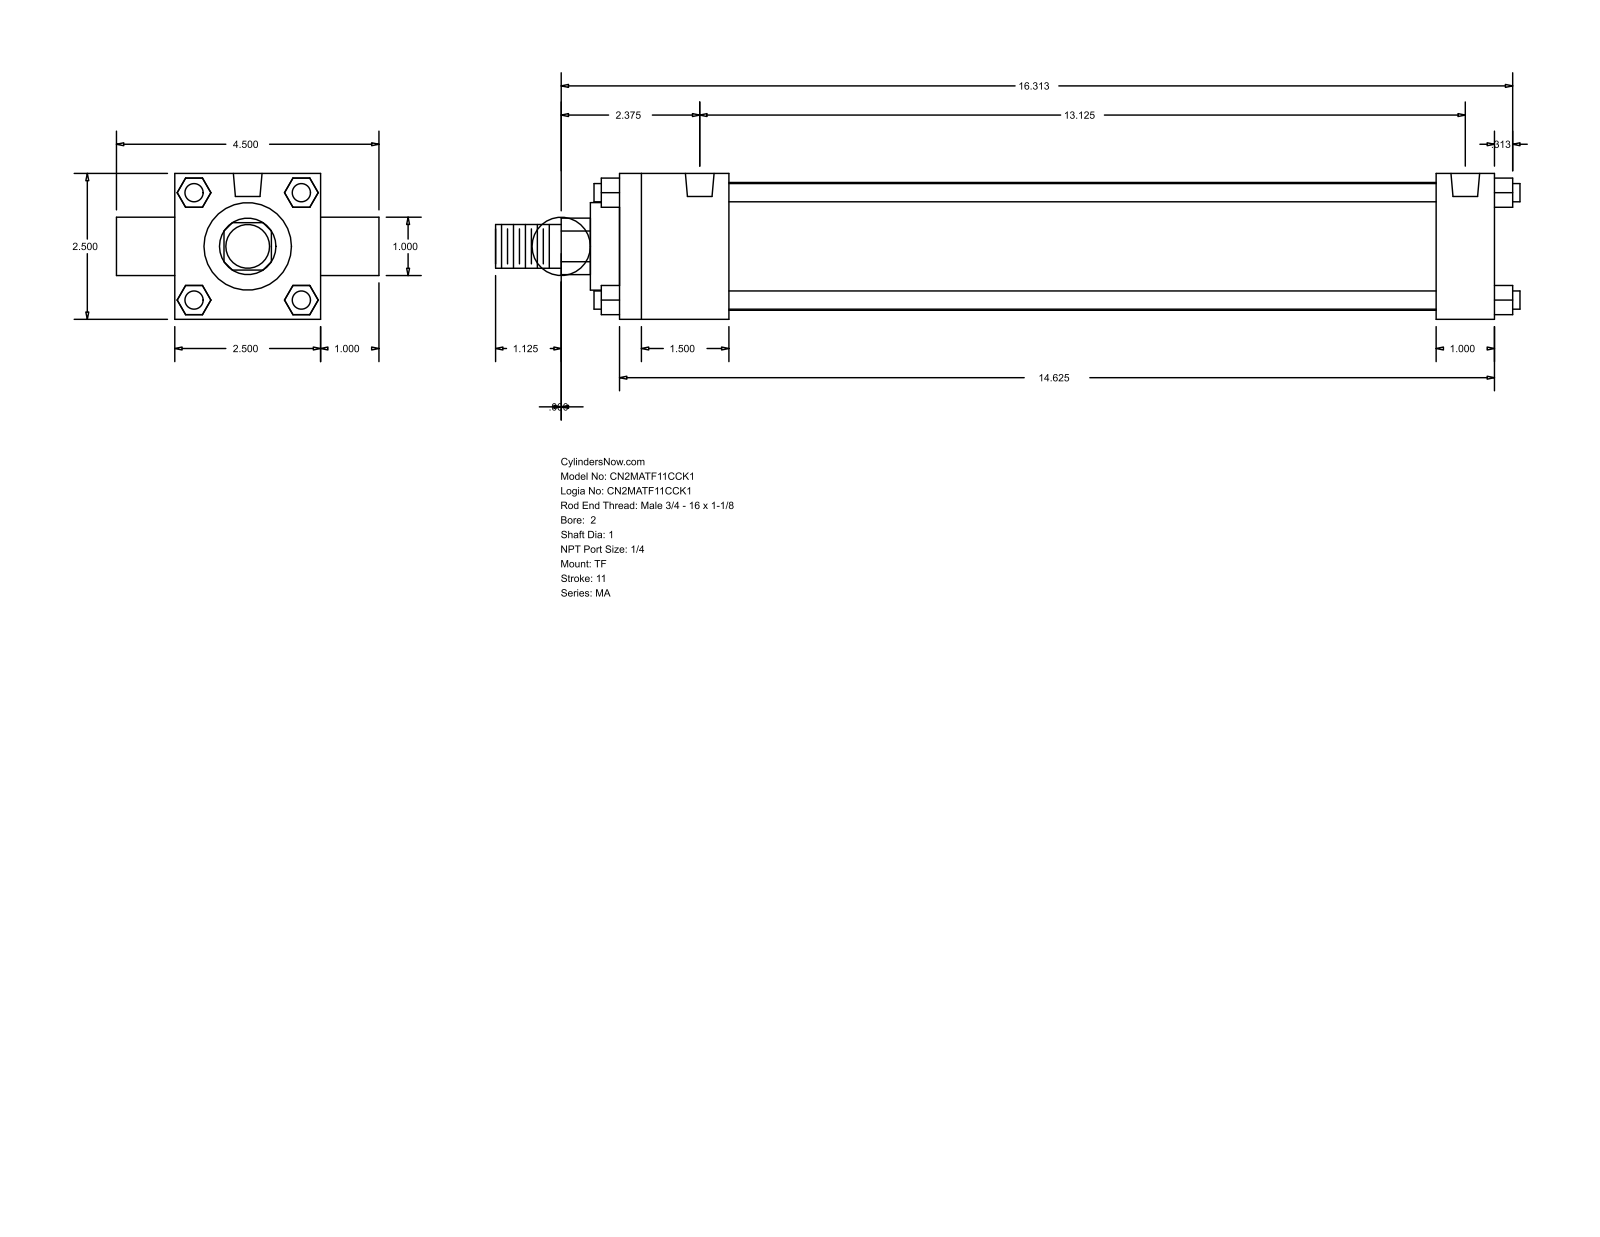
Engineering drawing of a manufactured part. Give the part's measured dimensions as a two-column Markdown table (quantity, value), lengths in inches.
| quantity | value |
| --- | --- |
| part name | MA_TF__0200_1 |
| STEP written by | GSSL Pune (CONFIG_CONTROL_DESIGN) |
| units | inches |
| bodies | 0 solids, 120 faces (92 planar, 28 cylindrical, 0 other) |
| overall size | 17.563 × 4.5 × 2.5 |
| round holes (diameter × count) | 0.313 × 3, 0.492 × 2 |
| round bosses / shafts (diameter × count) | 0.313 × 4, 1 × 2, 2.19 × 1, 1.5 × 1, 0.75 × 1 |
| partial cylindrical surfaces (radius × count) | 0.484 × 1 |
| main face-to-face distances | 2.5, 1, 15, 0.5, 1.875, 14, 12.125, 13.125, 3.5, 1.593 |
| hole center spacings | 13.125 |
